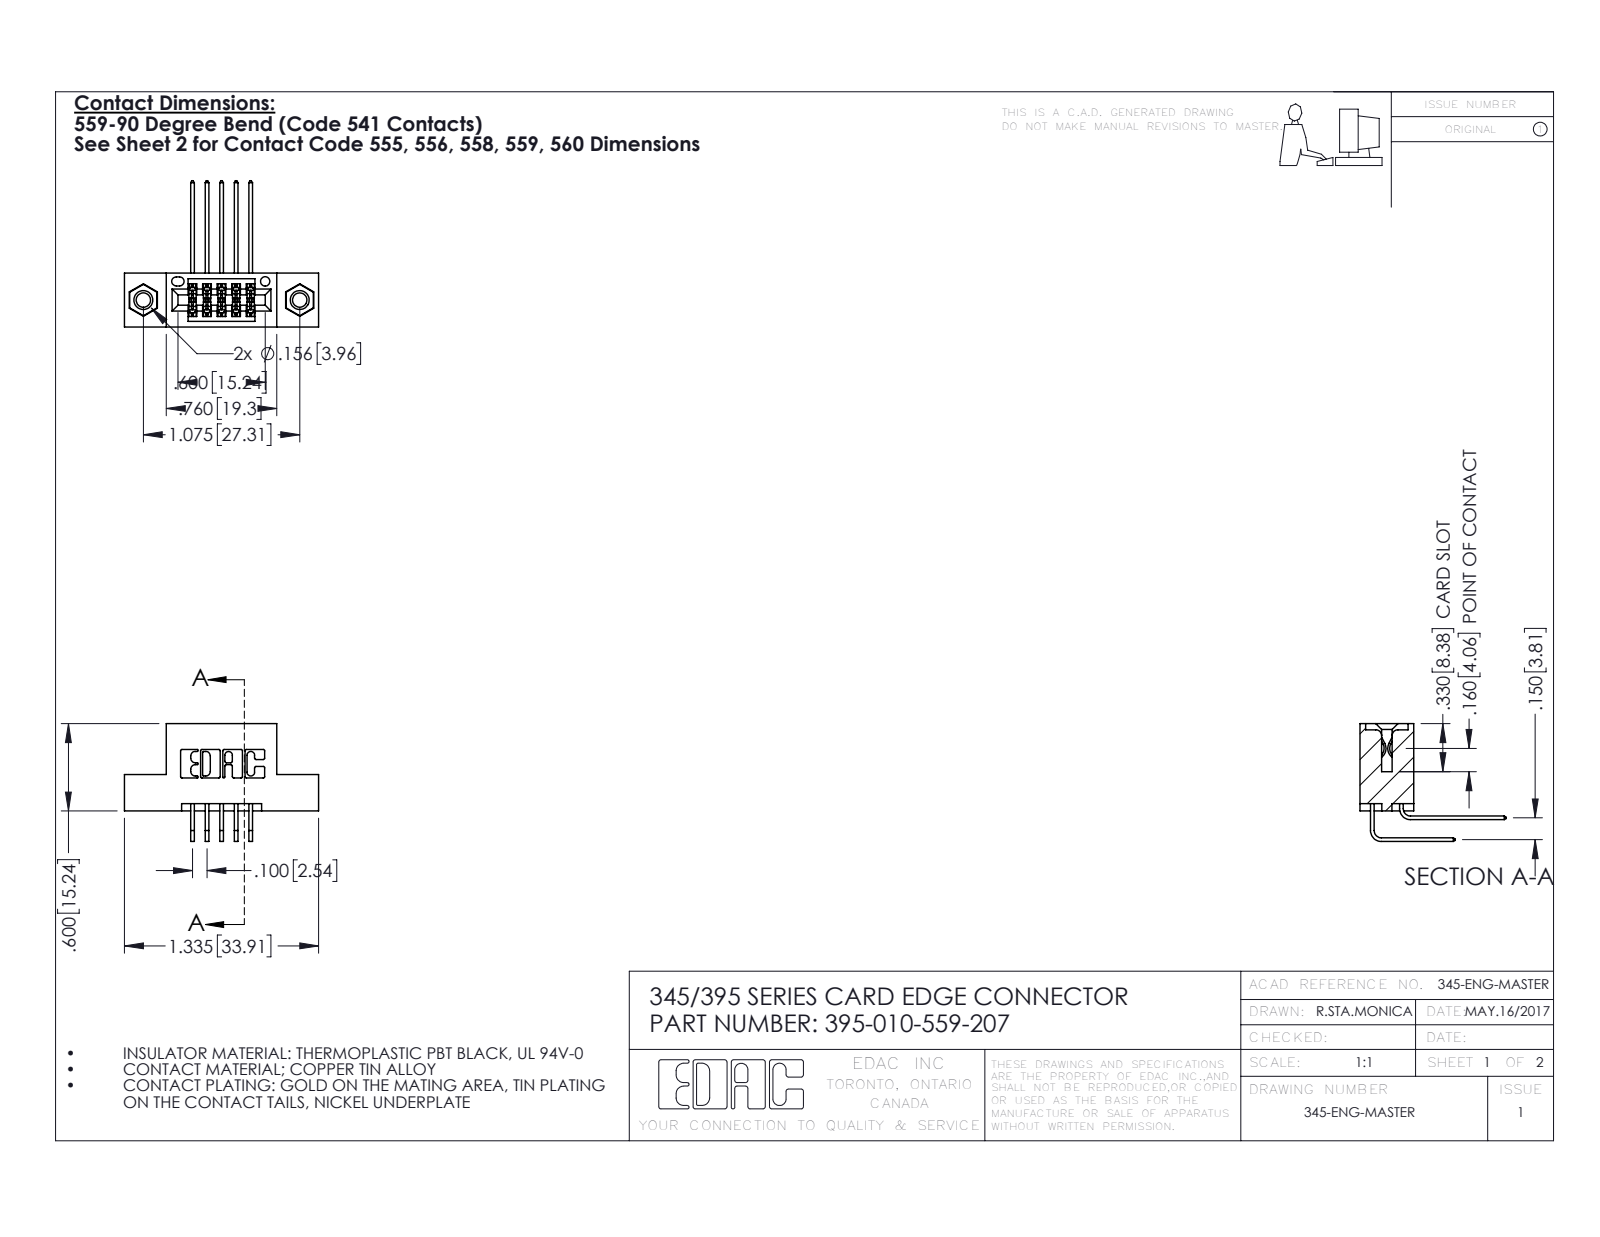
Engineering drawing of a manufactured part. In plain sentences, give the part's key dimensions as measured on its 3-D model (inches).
The part is named "395-010-559-207; 345-292-001_559 Tail - 2; 345-292-001_558 559 Tail - 1; 345-250-001_345-250-005-103 (+1 more)". Its 3-D file was written by "SolidWorks 2016 (CONFIG_CONTROL_DESIGN)". It is 13 solids with 706 faces: 462 planar, 228 cylindrical and 16 other. Overall it measures 1.335 by 1.005 by 0.809 inches. Its volume is 0.183 cubic inches and its surface area 6.214 square inches. Round holes: 2 of diameter 0.098, 2 of diameter 0.125, 2 of diameter 0.156, 1 of diameter 0.064. Round bosses or shafts: 2 of diameter 0.155. Partial cylindrical surfaces (rounded edges, fillets, slot ends): 22 of radius 0.01, 16 of radius 0.006, 6 of radius 0.007, 6 of radius 0.031, 3 of radius 0.026, 2 of radius 0.014, 2 of radius 0.019, 2 of radius 0.022. The main face-to-face distances are 0.2, 0.1, 0.37, 0.072, 0.298, 0.15, 0.098, 0.272, 0.025, 0.3. The hole center spacings are 0.27, 0.847, 1.075.
